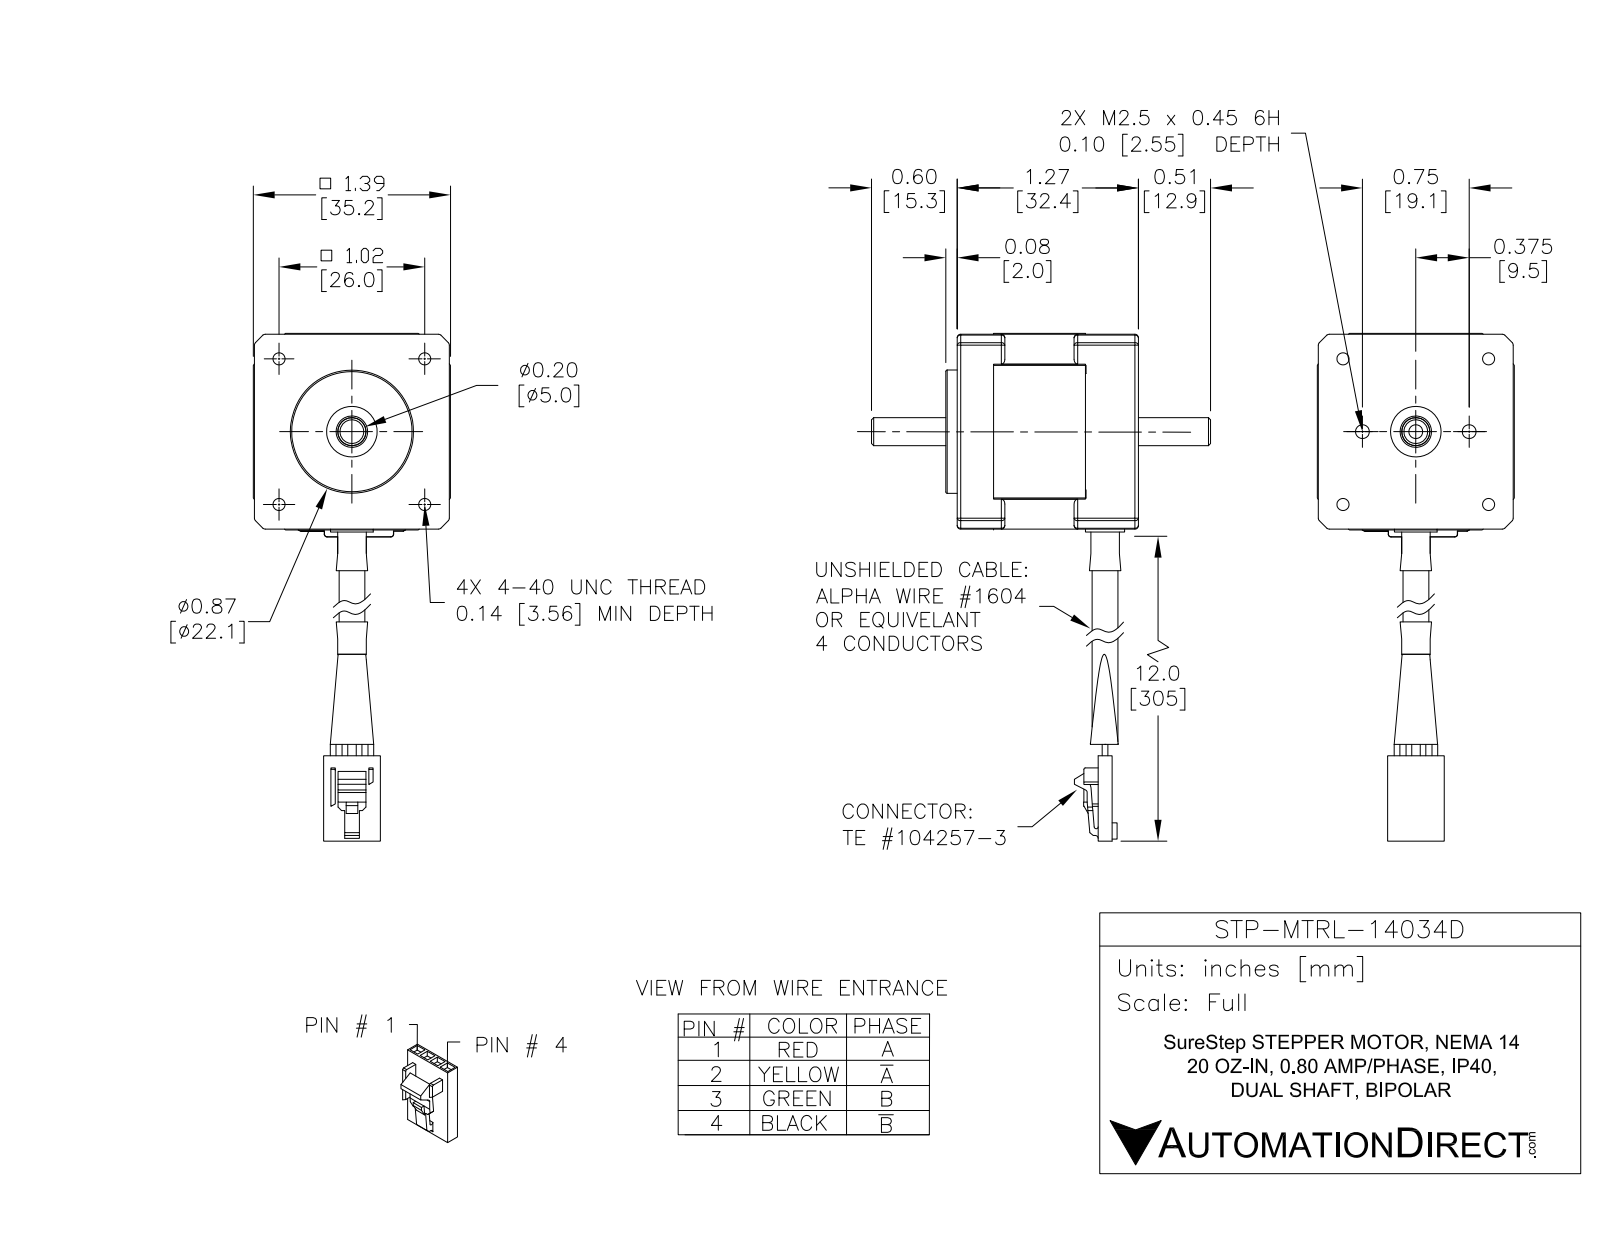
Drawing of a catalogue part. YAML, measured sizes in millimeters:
part_name: "STP-MTRL-14034D"
step_written_by: "SolidWorks 2017 (AUTOMOTIVE_DESIGN)"
units: millimeters
bodies: {solids: 12, faces: 575, planar: 292, cylindrical: 181, other: 102}
overall_size: [341.6, 60.5, 35.1]
volume: 23150
surface_area: 25030
round_holes:
  - {diameter: 5.7, count: 4}
  - {diameter: 2, count: 2}
  - {diameter: 2.2, count: 2}
  - {diameter: 2.2, count: 2}
  - {diameter: 5, count: 1}
  - {diameter: 5.1, count: 1}
  - {diameter: 7.1, count: 1}
  - {diameter: 7.2, count: 1}
  - {diameter: 8.1, count: 1}
  - {diameter: 10.7, count: 1}
  - {diameter: 13.2, count: 1}
  - {diameter: 16, count: 1}
round_bosses_or_shafts:
  - {diameter: 1, count: 4}
  - {diameter: 5.2, count: 3}
  - {diameter: 1.3, count: 2}
  - {diameter: 22, count: 1}
  - {diameter: 18.3, count: 1}
  - {diameter: 12.1, count: 1}
  - {diameter: 7.8, count: 1}
  - {diameter: 7.8, count: 1}
partial_cylinders:
  - {radius: 0.6, count: 24}
  - {radius: 0.5, count: 10}
  - {radius: 0.3, count: 3}
  - {radius: 0.4, count: 1}
  - {radius: 2.5, count: 1}
  - {radius: 20.2, count: 1}
  - {radius: 20.3, count: 1}
  - {radius: 21.1, count: 1}
face_to_face_distances: [34.8, 35, 1.7, 33.1, 33.3, 1.8, 31.5, 2.9, 35.1, 32.4]
hole_center_spacings: [26, 13.5, 18.4, 26, 36.8, 9.5, 9.5, 19.1]
